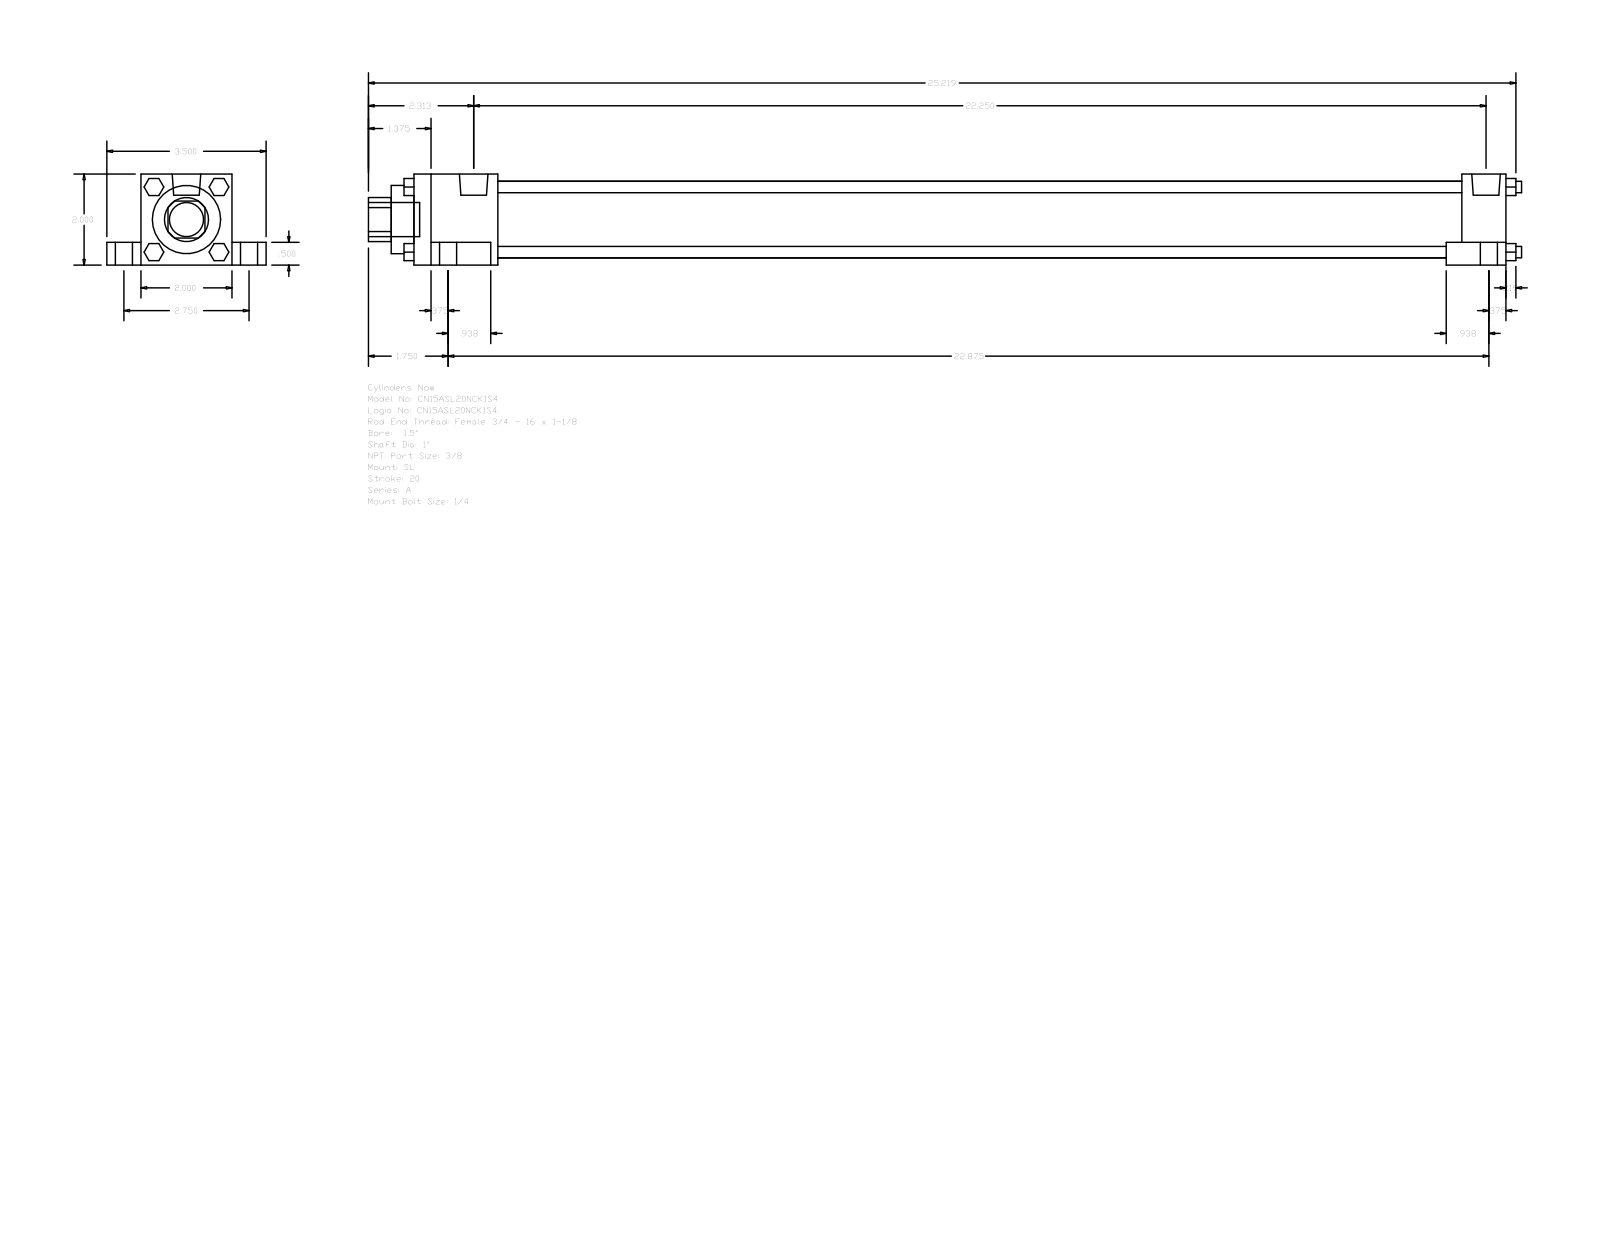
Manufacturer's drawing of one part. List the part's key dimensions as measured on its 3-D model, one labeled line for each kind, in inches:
Part name (STEP PRODUCT): A_SL__0150_1
STEP written by: GSSL Pune (CONFIG_CONTROL_DESIGN)
Units: inches
Bodies: 0 solids, 148 faces (112 planar, 36 cylindrical, 0 other)
Overall size (bounding box): 25.344 × 3.5 × 2
Round holes (diameter × count): ⌀1 ×1, ⌀1.5 ×1, ⌀1.69 ×1
Round bosses / shafts (diameter × count): ⌀0.625 ×4, ⌀0.375 ×4, ⌀0.25 ×4, ⌀0.219 ×4, ⌀0.627 ×2, ⌀0.75 ×1
Partial cylindrical surfaces — rounded edges, fillets, slot ends (radius × count): R0.484 ×1
Main face-to-face distances: 2, 0.5, 1.5, 0.75, 2.75, 0.375, 24, 1.313, 23.031, 0.969
